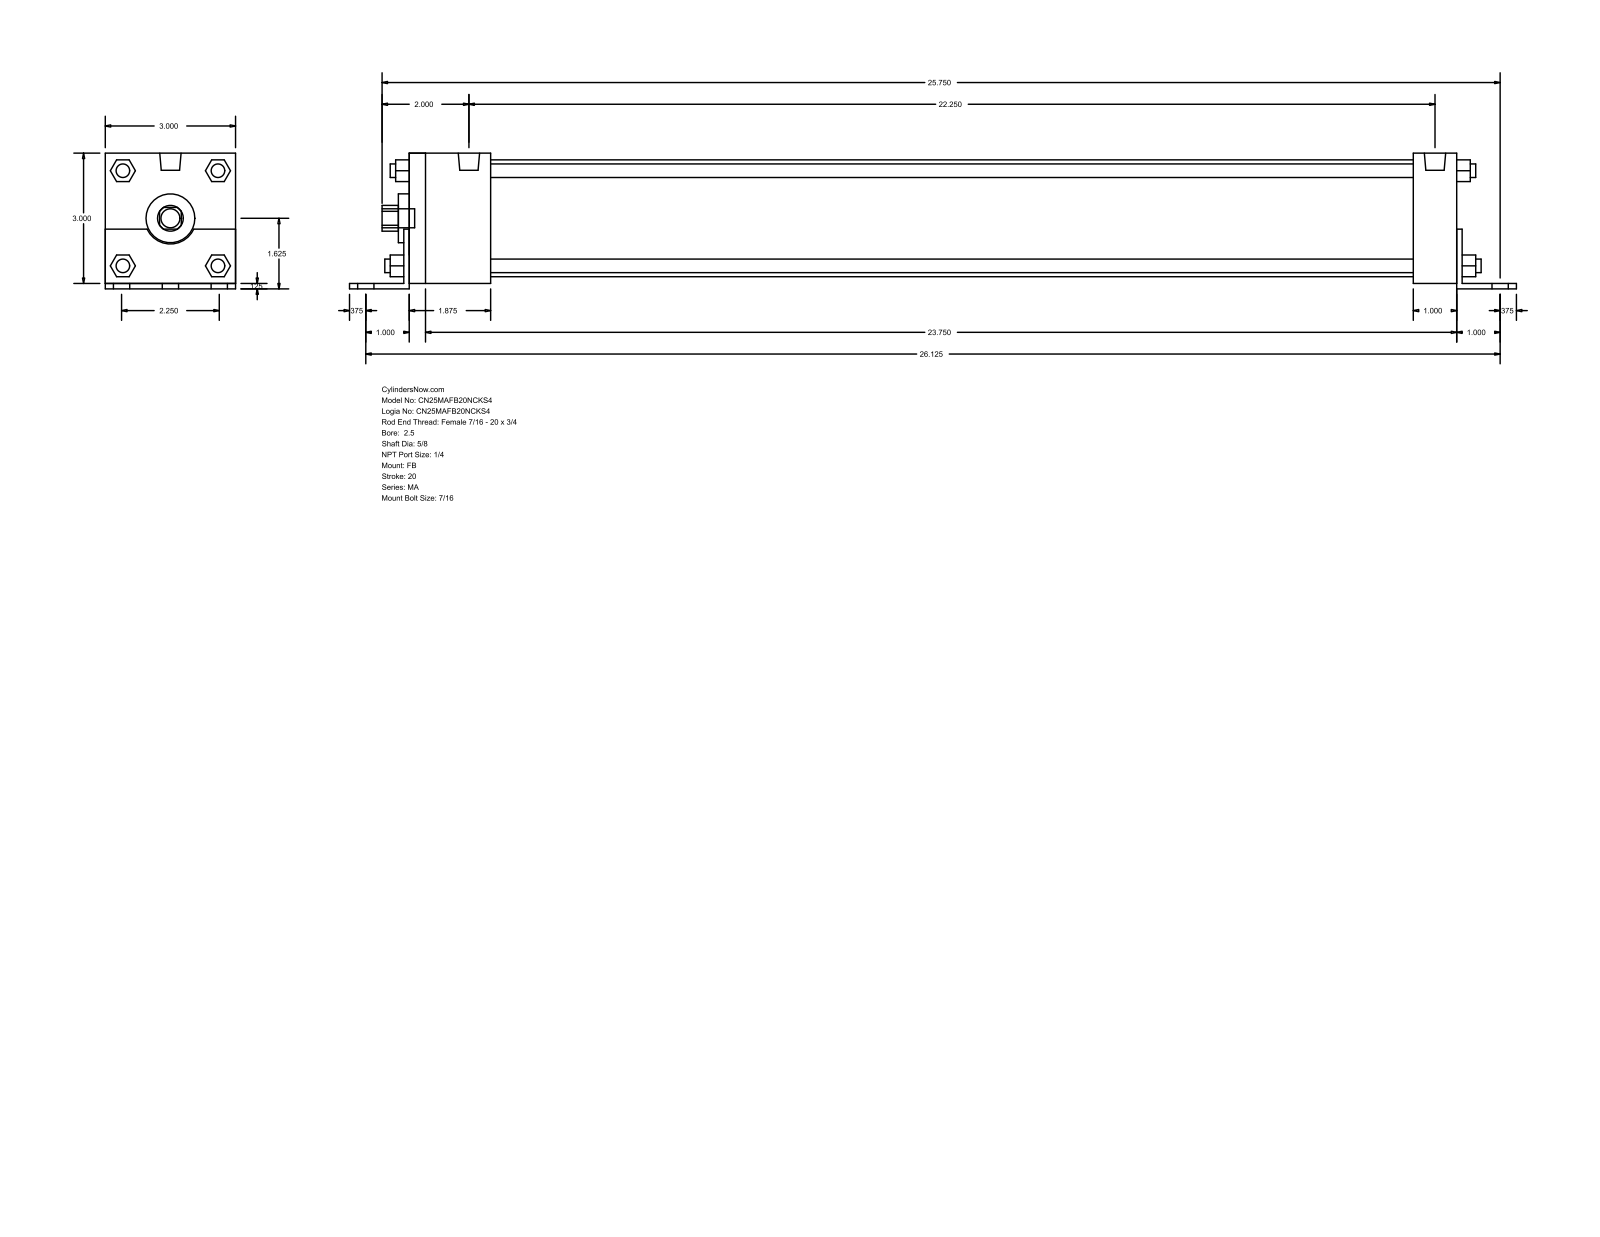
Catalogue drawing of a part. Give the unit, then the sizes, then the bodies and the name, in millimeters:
Units: millimetres
Overall size (bounding box): 682.62 × 79.38 × 76.2
Round holes (diameter × count): ⌀15.88 ×1, ⌀28.57 ×1, ⌀68.33 ×1
Round bosses / shafts (diameter × count): ⌀7.94 ×8, ⌀11.11 ×7, ⌀12.49 ×2
Partial cylindrical surfaces — rounded edges, fillets, slot ends (radius × count): R7.54 ×1, R15.05 ×1
Main face-to-face distances: 76.2, 3.17, 79.37, 3.18, 615.95, 612.77, 28.58, 47.62, 25.4, 619.13
Bodies: 0 solids, 140 faces (105 planar, 35 cylindrical, 0 other)
Part name (STEP PRODUCT): MA_FB__0250_0.625
STEP written by: GSSL Pune (CONFIG_CONTROL_DESIGN)
